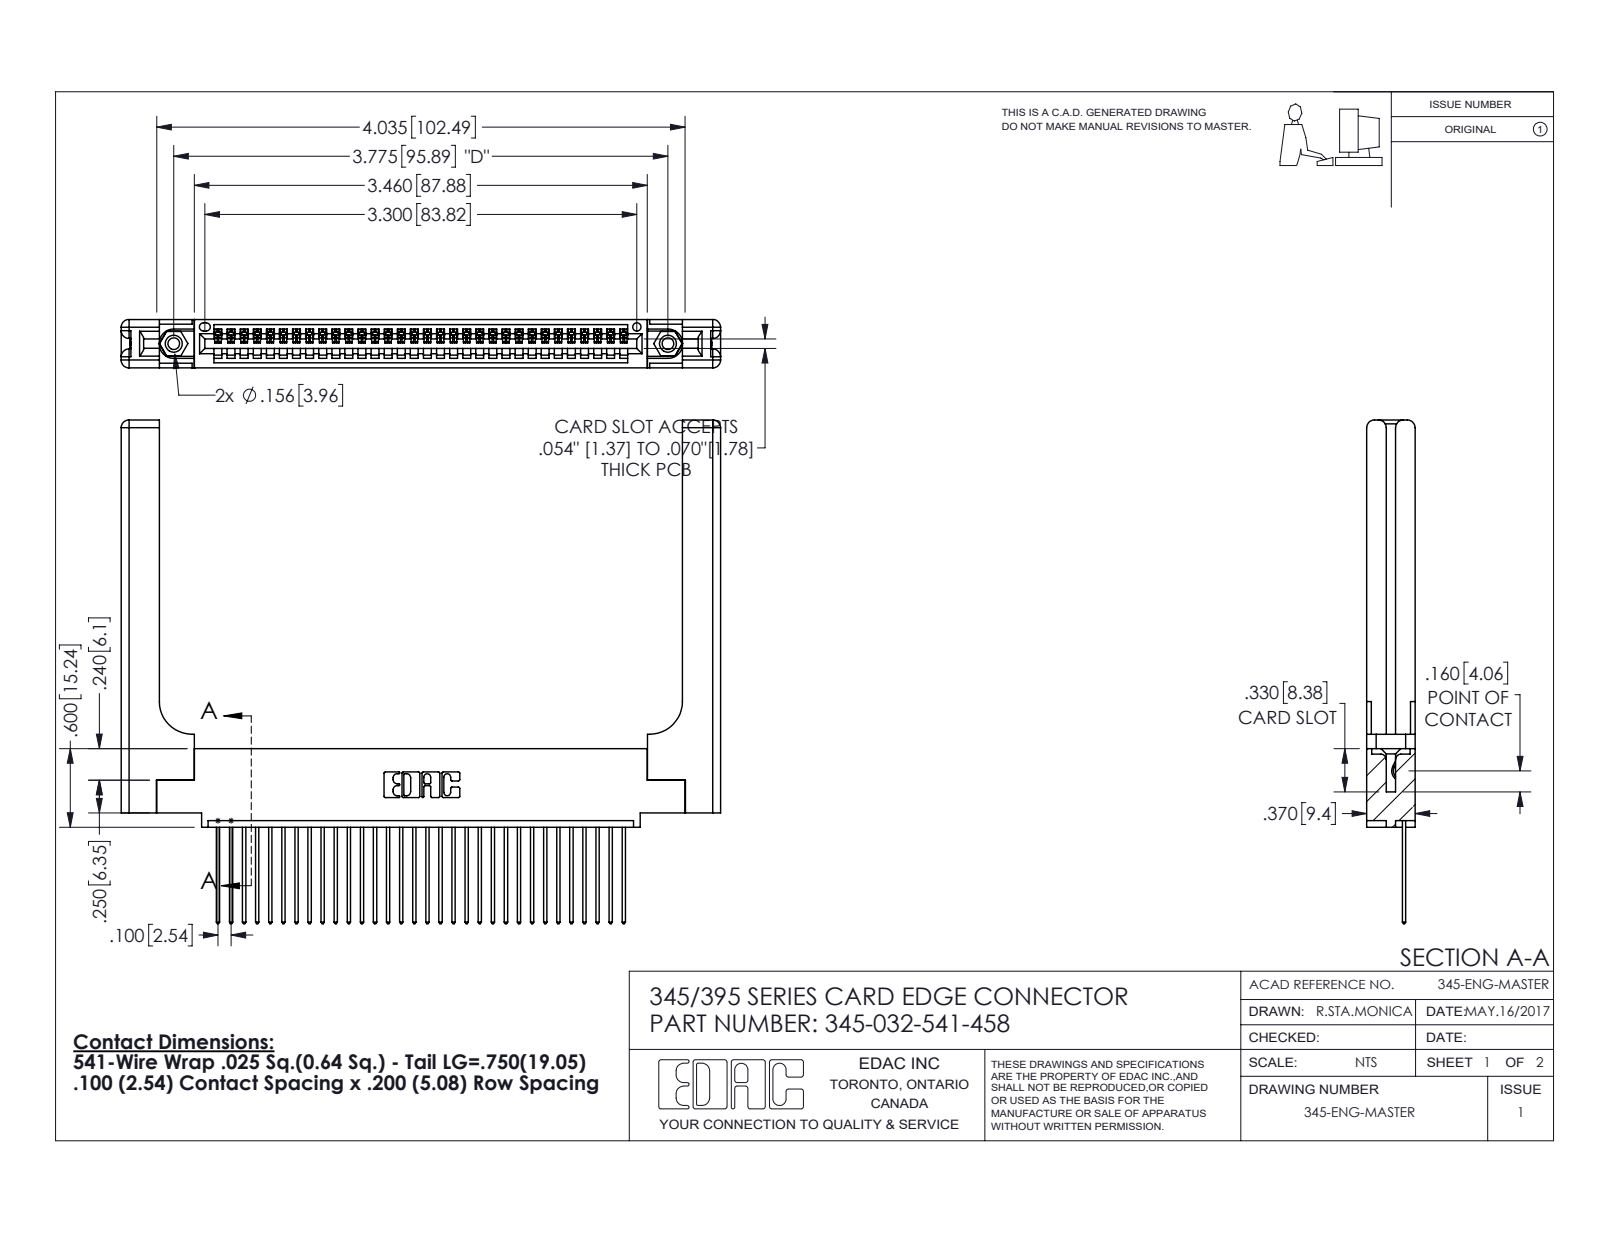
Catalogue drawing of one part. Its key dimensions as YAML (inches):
part_name: "345-250-001_345-250-001-102; 345-220-058_345-220-058; 345-292-001_345-293-141; 345-032-541-458 (+1 more)"
step_written_by: "SolidWorks 2016 (CONFIG_CONTROL_DESIGN)"
units: inches
bodies: {solids: 37, faces: 2242, planar: 1512, cylindrical: 670, other: 60}
overall_size: [4.579, 3.847, 0.37]
volume: 1.19
surface_area: 31.76
round_holes:
  - {diameter: 0.089, count: 2}
  - {diameter: 0.125, count: 2}
  - {diameter: 0.156, count: 2}
  - {diameter: 0.064, count: 1}
round_bosses_or_shafts:
  - {diameter: 0.155, count: 2}
partial_cylinders:
  - {radius: 0.006, count: 64}
  - {radius: 0.01, count: 64}
  - {radius: 0.01, count: 22}
  - {radius: 0.06, count: 16}
  - {radius: 0.007, count: 6}
  - {radius: 0.031, count: 6}
  - {radius: 0.026, count: 3}
  - {radius: 0.03, count: 2}
face_to_face_distances: [0.072, 0.37, 0.298, 0.098, 0.272, 0.025, 0.2, 0.148, 0.15, 0.077]
hole_center_spacings: [0.27, 3.54, 3.775]
